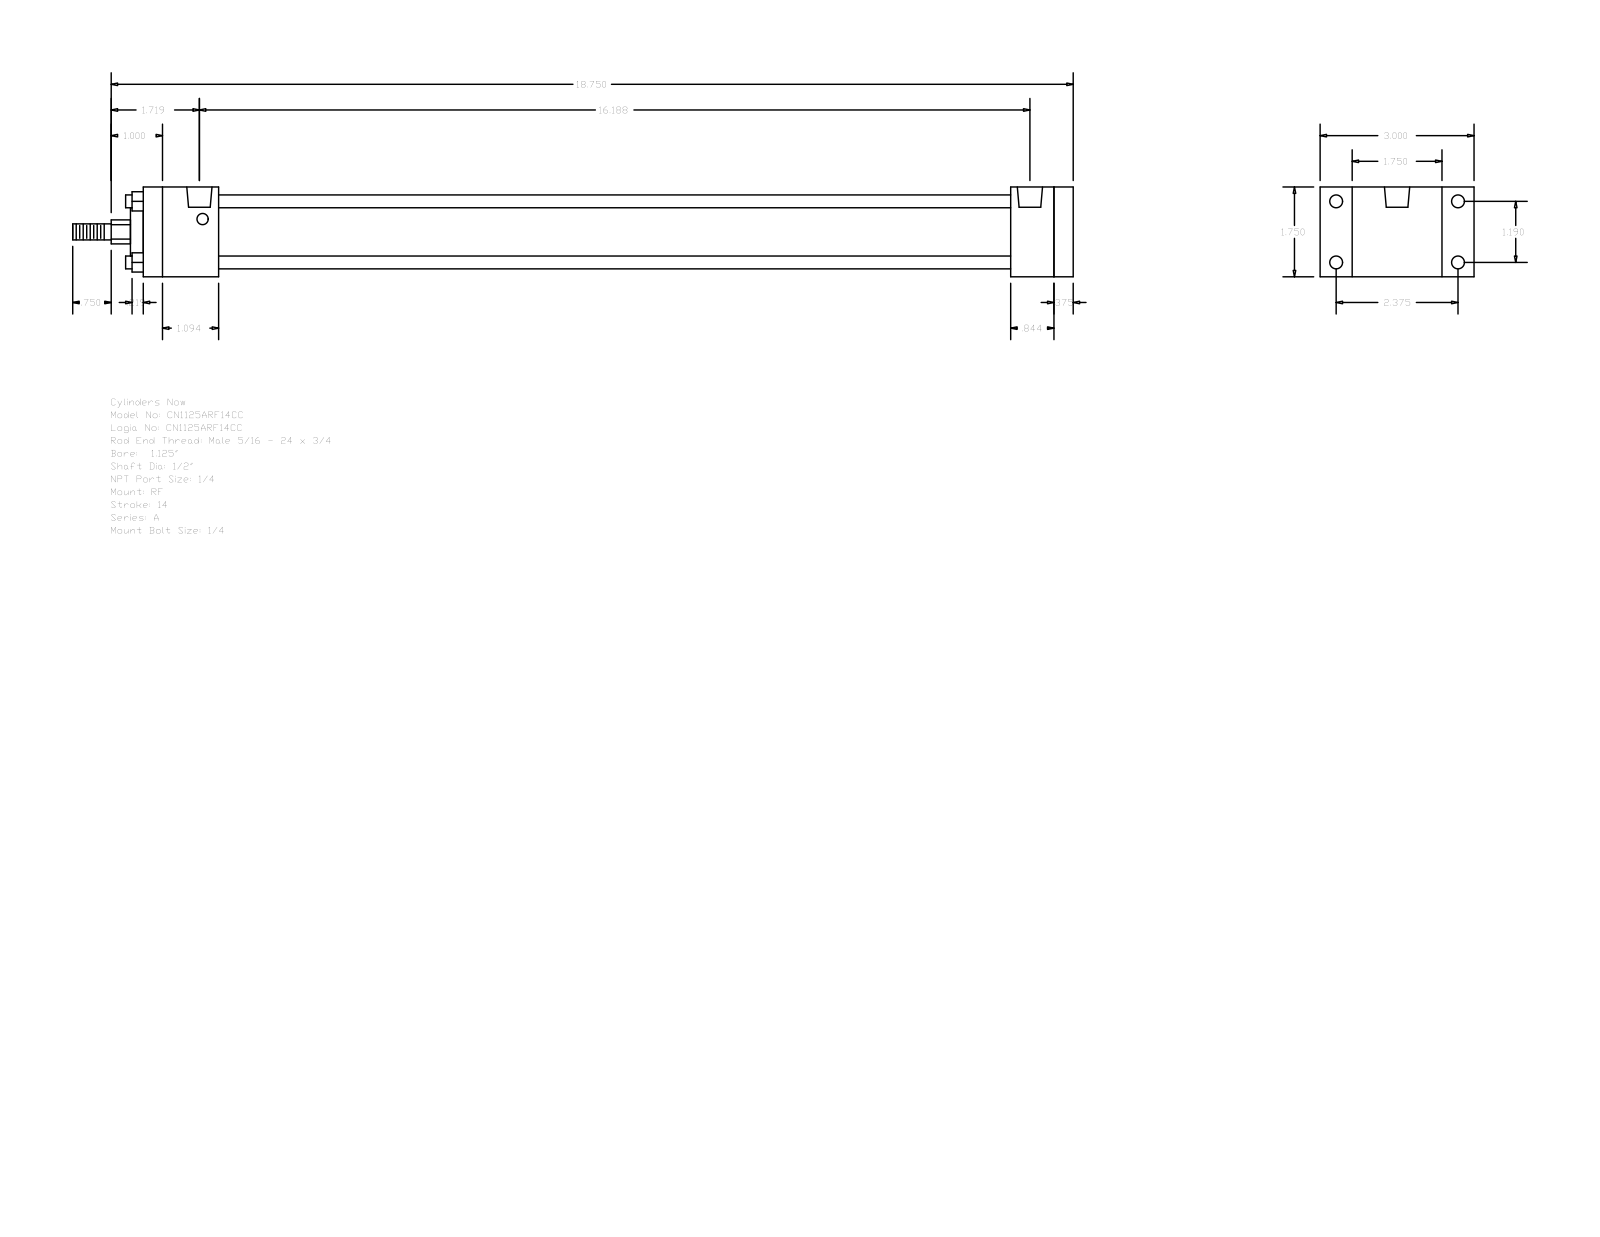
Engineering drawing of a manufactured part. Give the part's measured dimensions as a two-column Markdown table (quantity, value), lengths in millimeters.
| quantity | value |
| --- | --- |
| part name | A_RF__0112_0.5 |
| STEP written by | GSSL Pune (CONFIG_CONTROL_DESIGN) |
| units | millimeters |
| bodies | 0 solids, 92 faces (64 planar, 28 cylindrical, 0 other) |
| overall size | 495.3 × 76.2 × 44.45 |
| round holes (diameter × count) | 5.56 × 4, 6.35 × 4, 12.49 × 2 |
| round bosses / shafts (diameter × count) | 6.35 × 4, 31.88 × 1, 23.81 × 1, 12.7 × 1, 7.94 × 1 |
| partial cylindrical surfaces (radius × count) | 5.94 × 1 |
| main face-to-face distances | 44.46, 9.52, 450.85, 460.37, 37.3, 429.41, 392.11, 413.55, 423.07, 21.44 |
| hole center spacings | 30.22, 60.32, 67.47, 407.99, 1.58, 1.59, 409.57, 409.58 |
